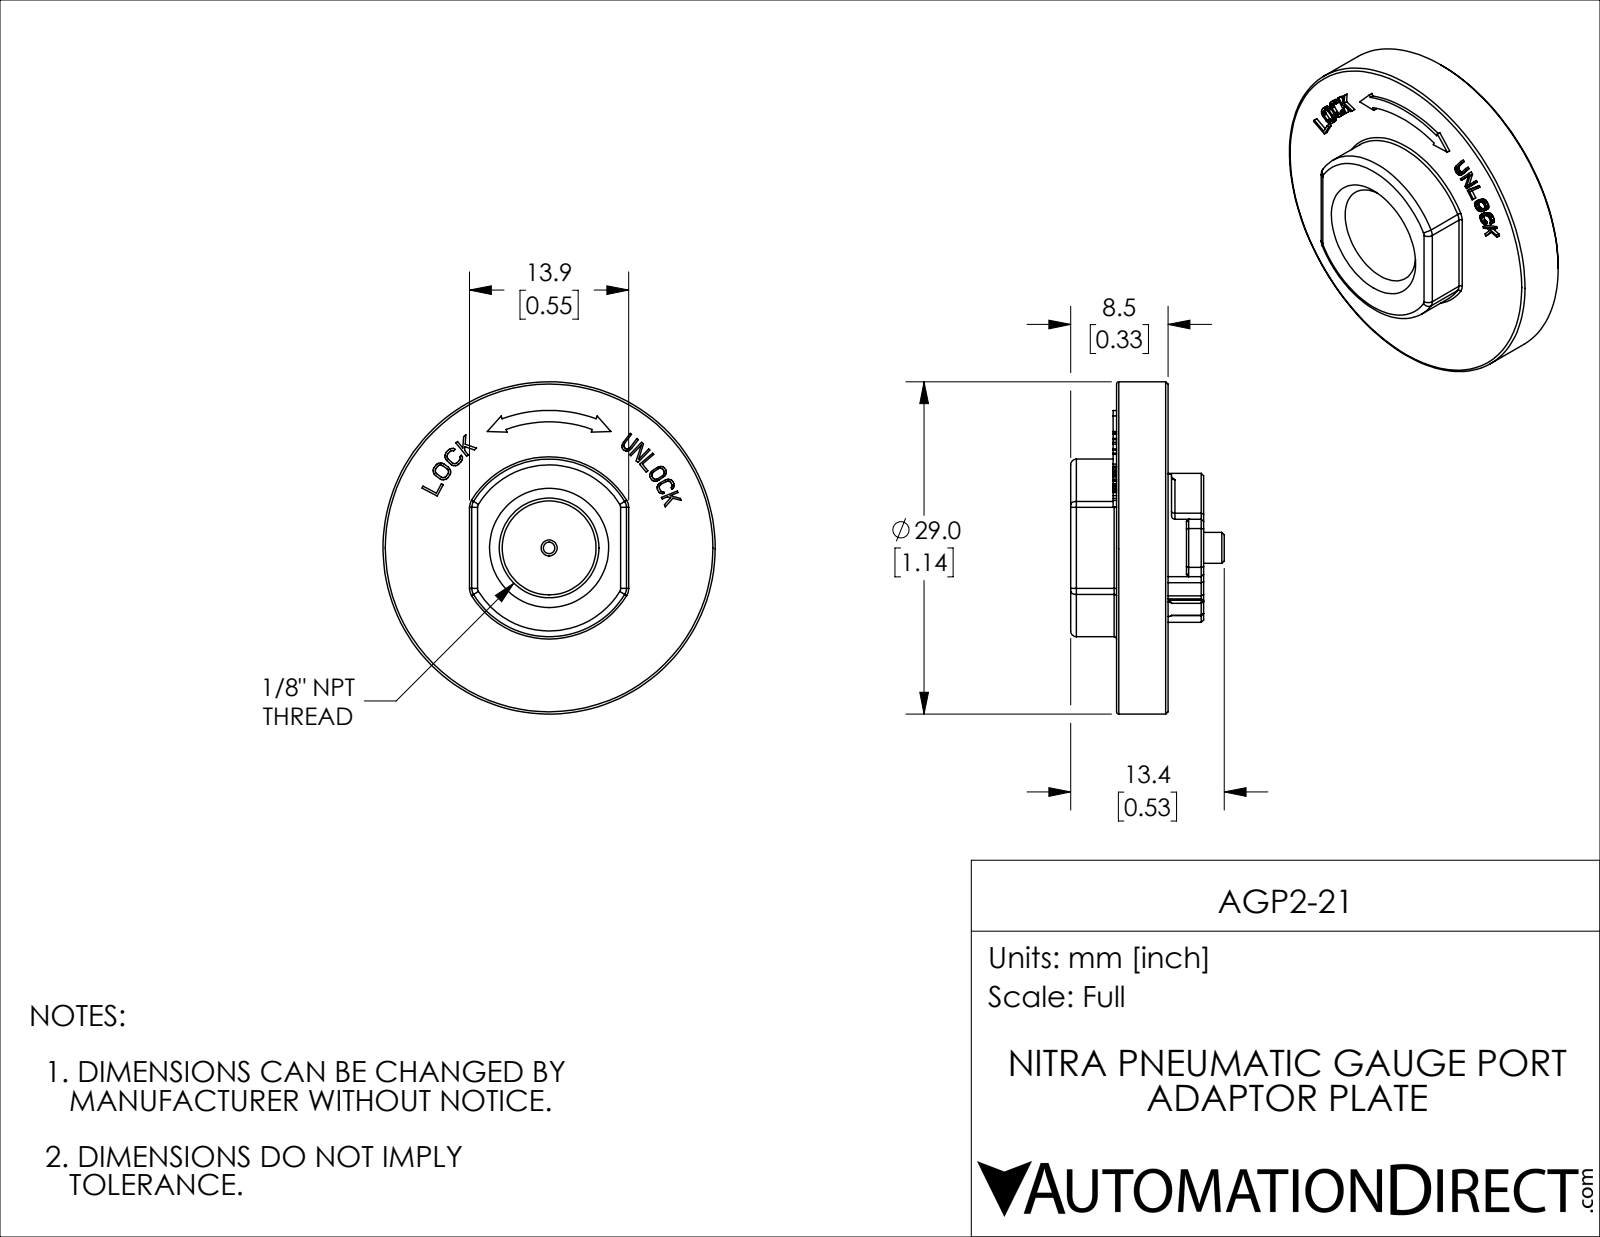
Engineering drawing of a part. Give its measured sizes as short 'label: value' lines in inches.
name: AGP2-21
written by: SolidWorks 2019 (CONFIG_CONTROL_DESIGN)
unit: in
bodies: 1 solid, 505 faces (303 planar, 88 cylindrical, 114 other)
size: 1.142 × 1.142 × 0.528
volume: 0.172 in³; area: 4.298 in²
holes: 1× ⌀0.039
bosses: 1× ⌀1.142, 1× ⌀0.106
rounds: 36× R0.008, 12× R0.039, 2× R0.02, 1× R0.256, 1× R0.276, 1× R0.305, 1× R0.354, 1× R0.433
face distances: 0.059, 0.118, 0.177, 0.24, 0.122, 0.299, 0.157, 0.217, 0.457, 0.335
